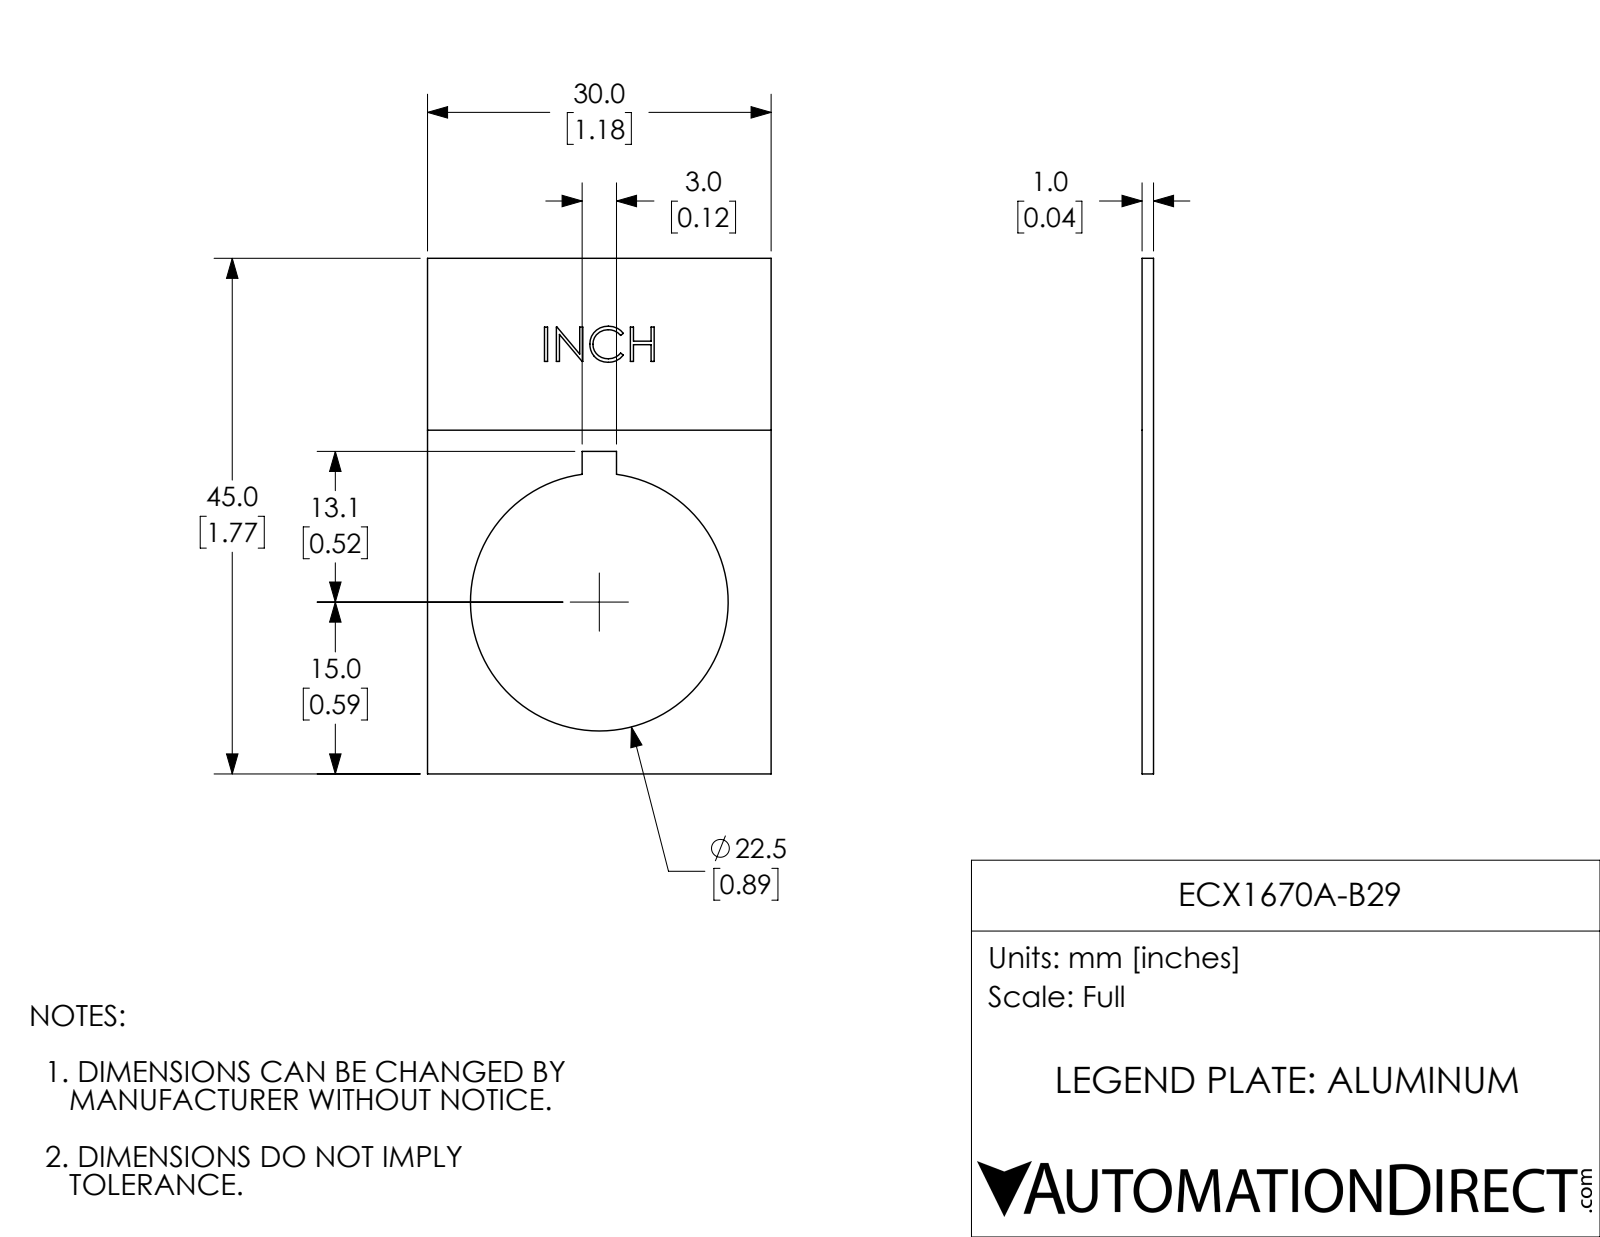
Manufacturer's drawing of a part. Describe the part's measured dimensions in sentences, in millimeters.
The part is named "ECX1670A-B29". Its 3-D file was written by "SolidWorks 2017 (AUTOMOTIVE_DESIGN)". It is 1 solid with 54 faces: 42 planar, 3 cylindrical and 9 other. Overall it measures 45 by 30 by 1 millimeters. Its volume is 950 cubic millimeters and its surface area 2 119 square millimeters. Round holes: 1 of diameter 22.5. The main face-to-face distances are 1, 30, 45, 1, 13.5, 16.5, 28.1, 16.8, 3, 9.3.
